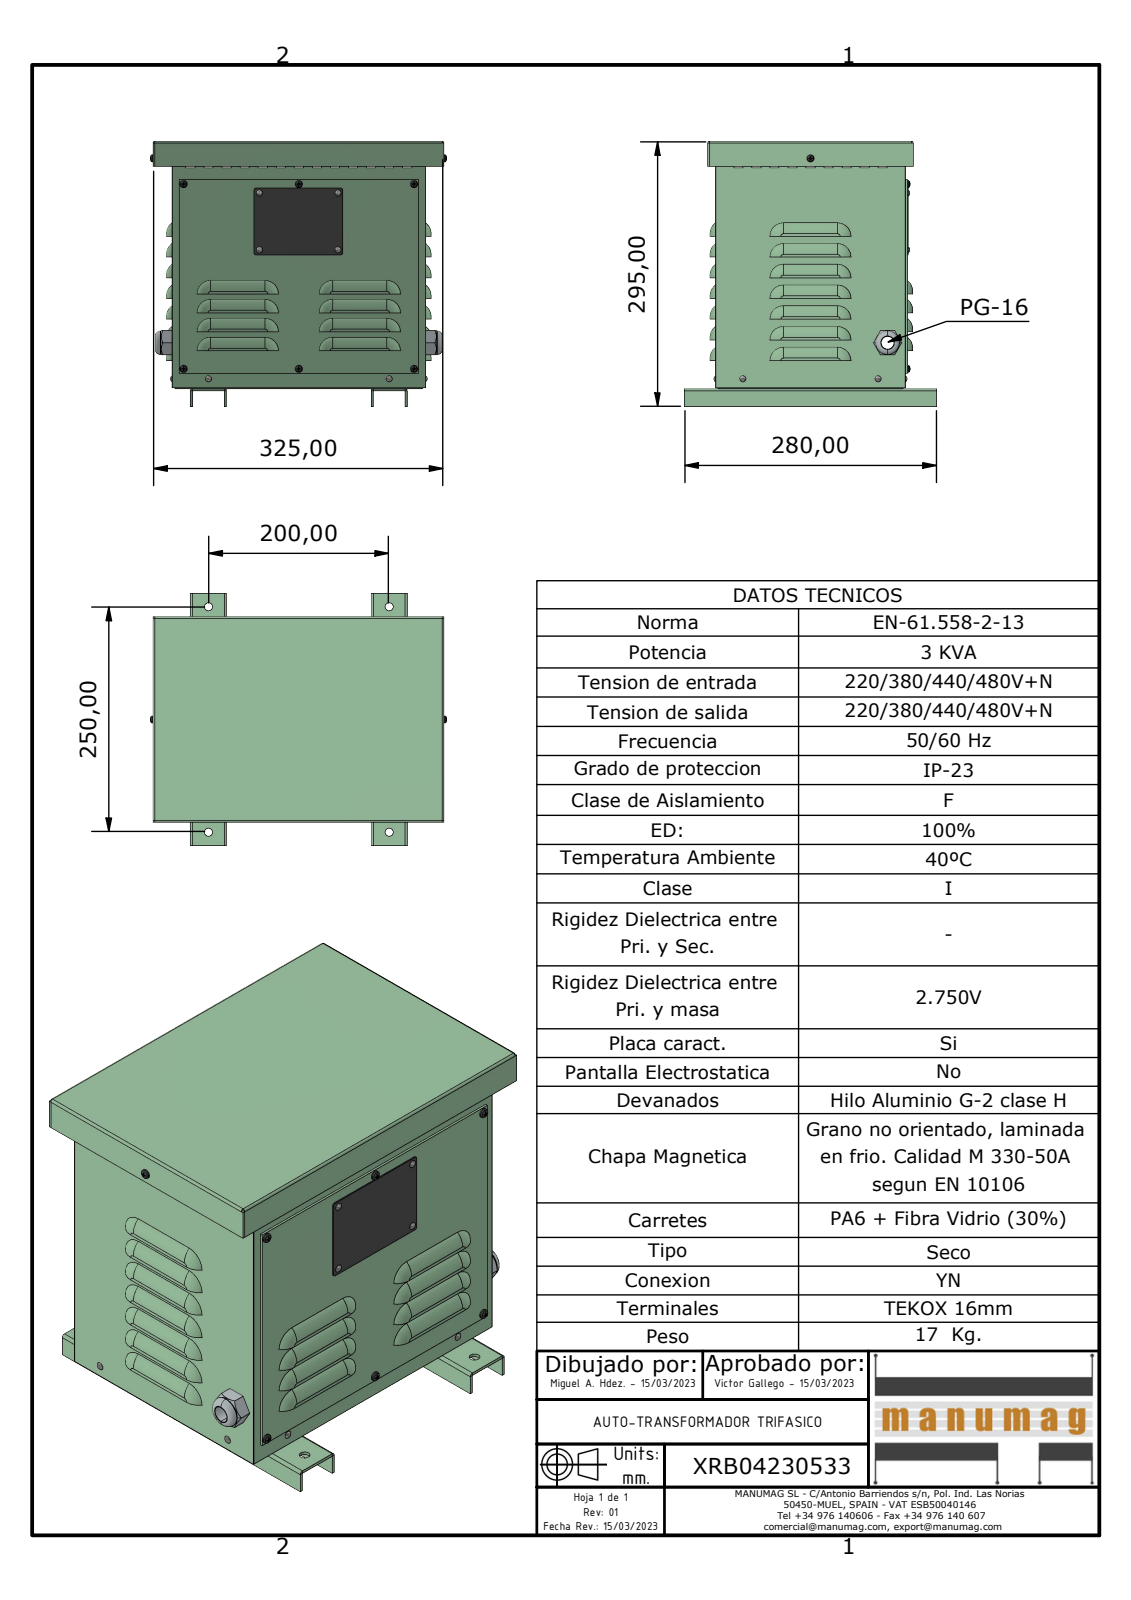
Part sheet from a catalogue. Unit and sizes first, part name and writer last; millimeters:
Units: millimetres
Overall size (bounding box): 328.13 × 294.5 × 280
Round holes (diameter × count): ⌀4.8 ×13, ⌀3 ×12, ⌀9 ×6, ⌀3.8 ×5, ⌀4 ×4, ⌀14 ×1, ⌀24 ×1
Round bosses / shafts (diameter × count): ⌀3.2 ×8, ⌀4 ×7, ⌀3.62 ×7, ⌀26 ×1, ⌀23 ×1, ⌀22.5 ×1
Partial cylindrical surfaces — rounded edges, fillets, slot ends (radius × count): R14 ×44, R4 ×25, R15 ×25, R0.5 ×9, R2 ×8, R4.5 ×8, R1.5 ×6, R1.5 ×4
Main face-to-face distances: 0.5, 2, 210.5, 280.5, 2.5, 1.5, 274.5, 272.5, 211, 213
Hole centre spacings: 127.5, 200, 241.42, 205, 29.62, 44.63, 47, 63
Volume: 827 636 mm³ · Surface area: 1 061 000 mm²
Bodies: 29 solids, 1436 faces (841 planar, 283 cylindrical, 312 other)
Part name (STEP PRODUCT): XRB04230533; JE003 - JE004 - JE005 EXPORT BASE; JE003 - JE004 - JE005 EXPORT PATA; JE003 - JE004 - JE005 EXPORT CUERPO (+6 more)
STEP written by: Autodesk Inventor 2023 (AUTOMOTIVE_DESIGN)
